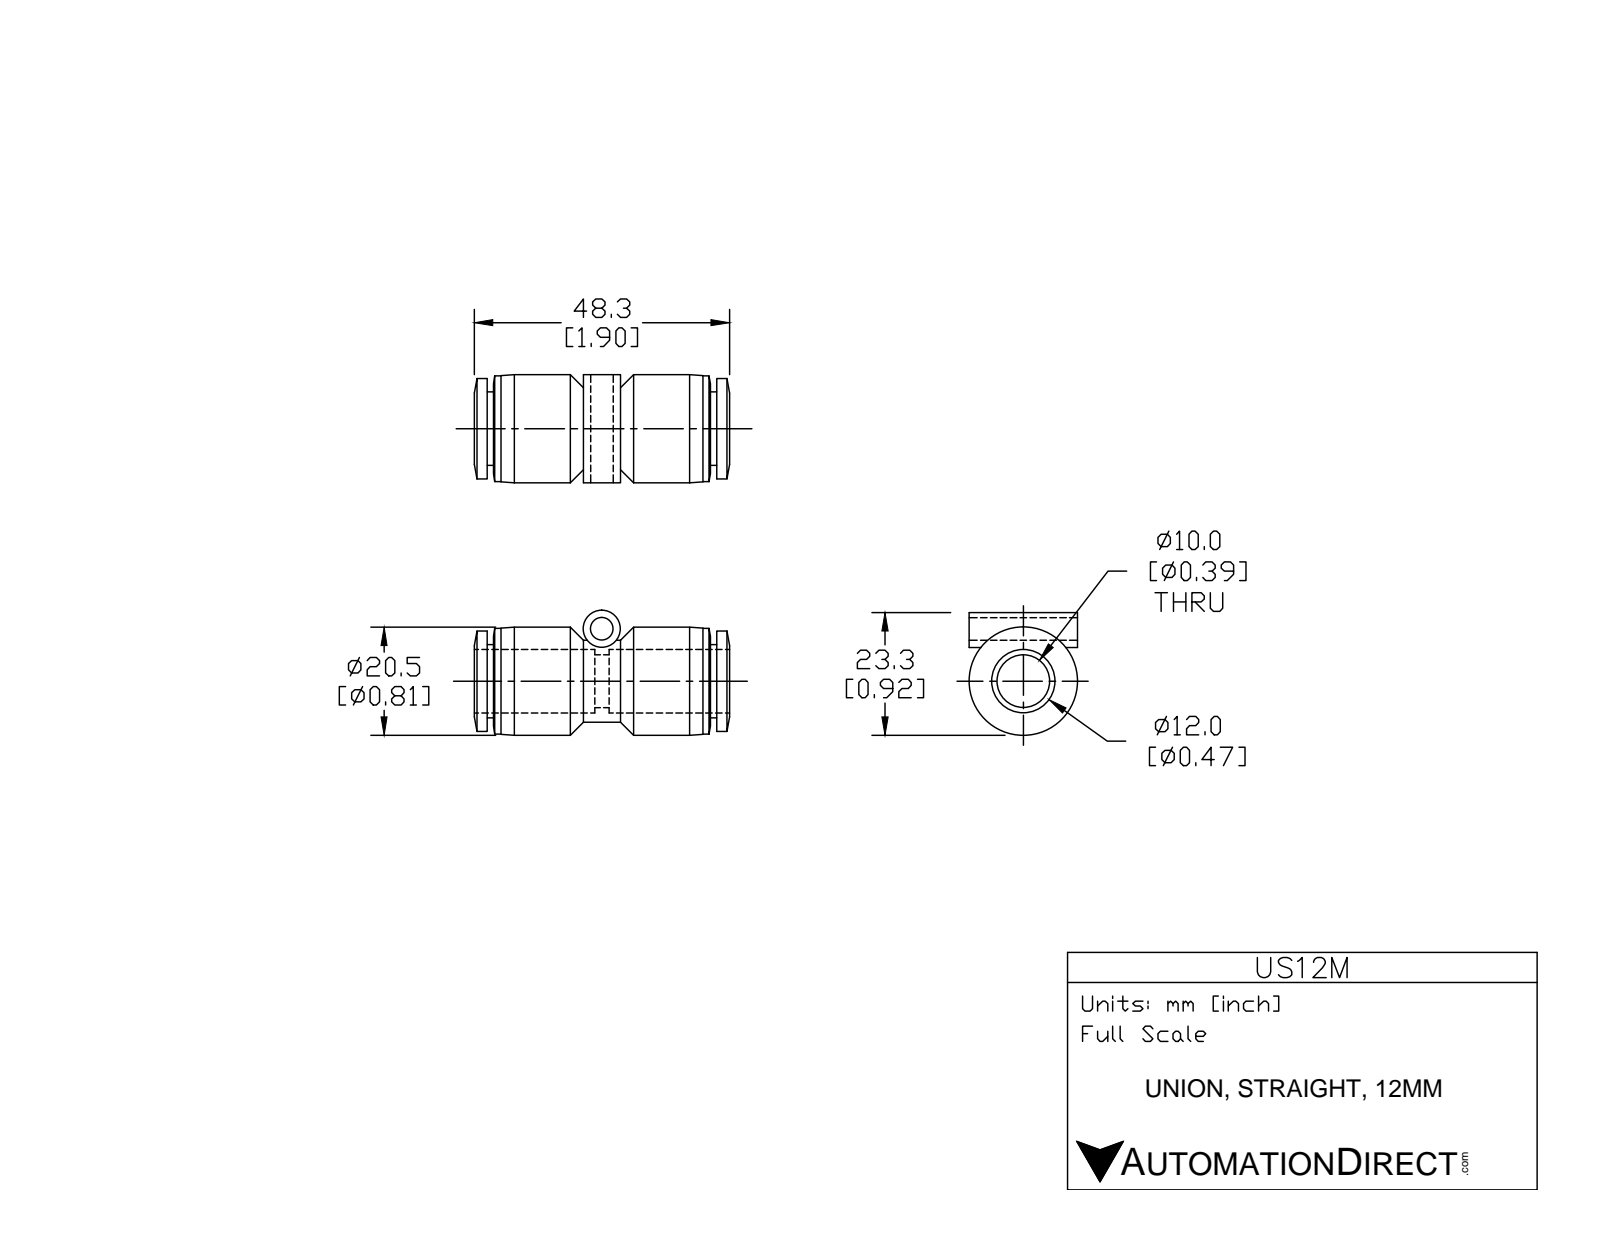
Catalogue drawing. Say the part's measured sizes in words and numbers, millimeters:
The part is named "US12M". Its 3-D file was written by "SolidWorks 2015 (CONFIG_CONTROL_DESIGN)". It is 1 solid with 48 faces: 8 planar, 28 cylindrical and 12 other. Overall it measures 48.3 by 23.65 by 20.5 millimeters. Its volume is 9 190 cubic millimeters and its surface area 6 172 square millimeters. Round holes: 1 of diameter 4.3, 1 of diameter 10, 1 of diameter 12. Round bosses or shafts: 1 of diameter 20.5, 1 of diameter 19, 1 of diameter 17, 1 of diameter 16, 1 of diameter 7. The main face-to-face distances are 1.46, 42.04, 43.5, 40.58, 20.4, 23.1, 18.94, 21.64, 2.7, 20.5.
